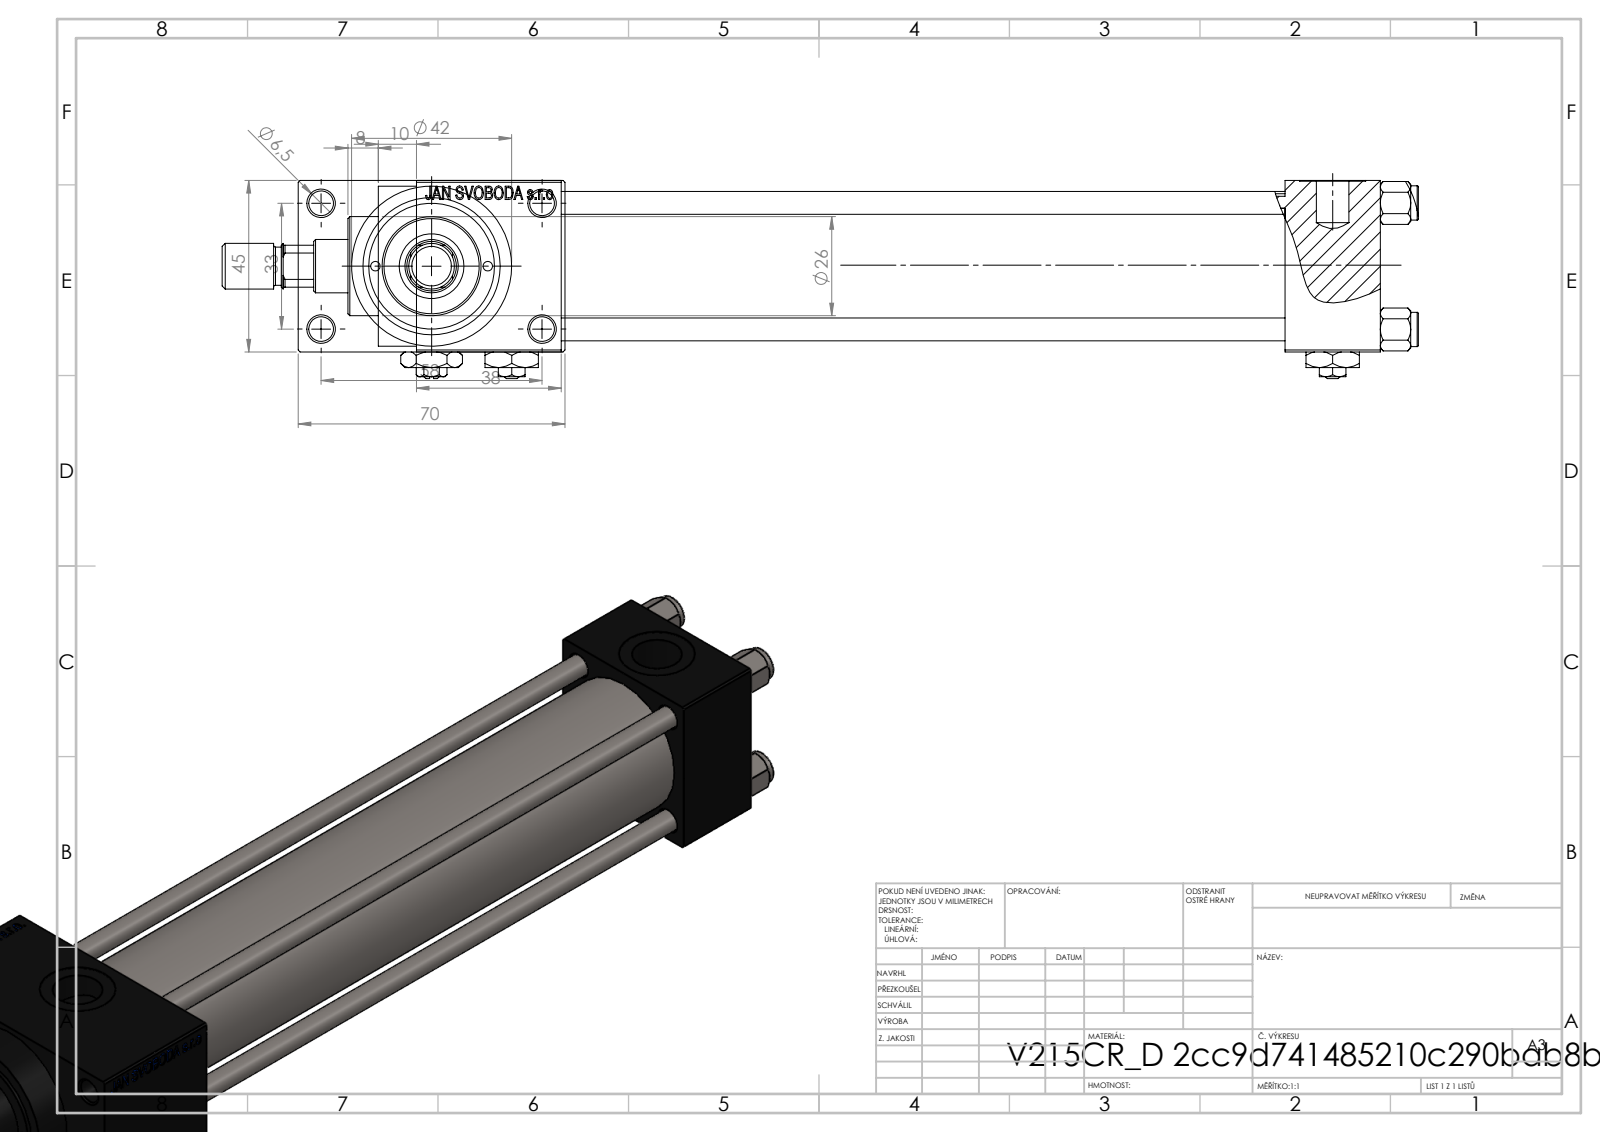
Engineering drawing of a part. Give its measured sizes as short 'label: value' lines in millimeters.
name: NUT_M5_D; V215CR_D_Body; V215_VC_A; V215CR_D_TYCINKA (+3 more)
written by: SolidWorks 2019 (CONFIG_CONTROL_DESIGN)
unit: mm
bodies: 14 solids, 1224 faces (548 planar, 108 cylindrical, 568 other)
size: 314 × 70 × 52
volume: 315 821 mm³; area: 124 957 mm²
holes: 5× ⌀6.5, 4× ⌀6, 2× ⌀2.5, 2× ⌀7, 2× ⌀13.16, 2× ⌀20, 1× ⌀14, 1× ⌀17, 1× ⌀24, 1× ⌀32, 1× ⌀33
bosses: 4× ⌀9, 1× ⌀42, 1× ⌀38, 1× ⌀26, 1× ⌀12, 1× ⌀10
rounds: 1× R6.5
face distances: 45, 25, 12.5, 57.5, 190, 215, 228, 70, 38, 253
hole spacings: 12.4, 16.7, 21.8, 23.48, 33.2, 33.37, 35.35, 35.47
